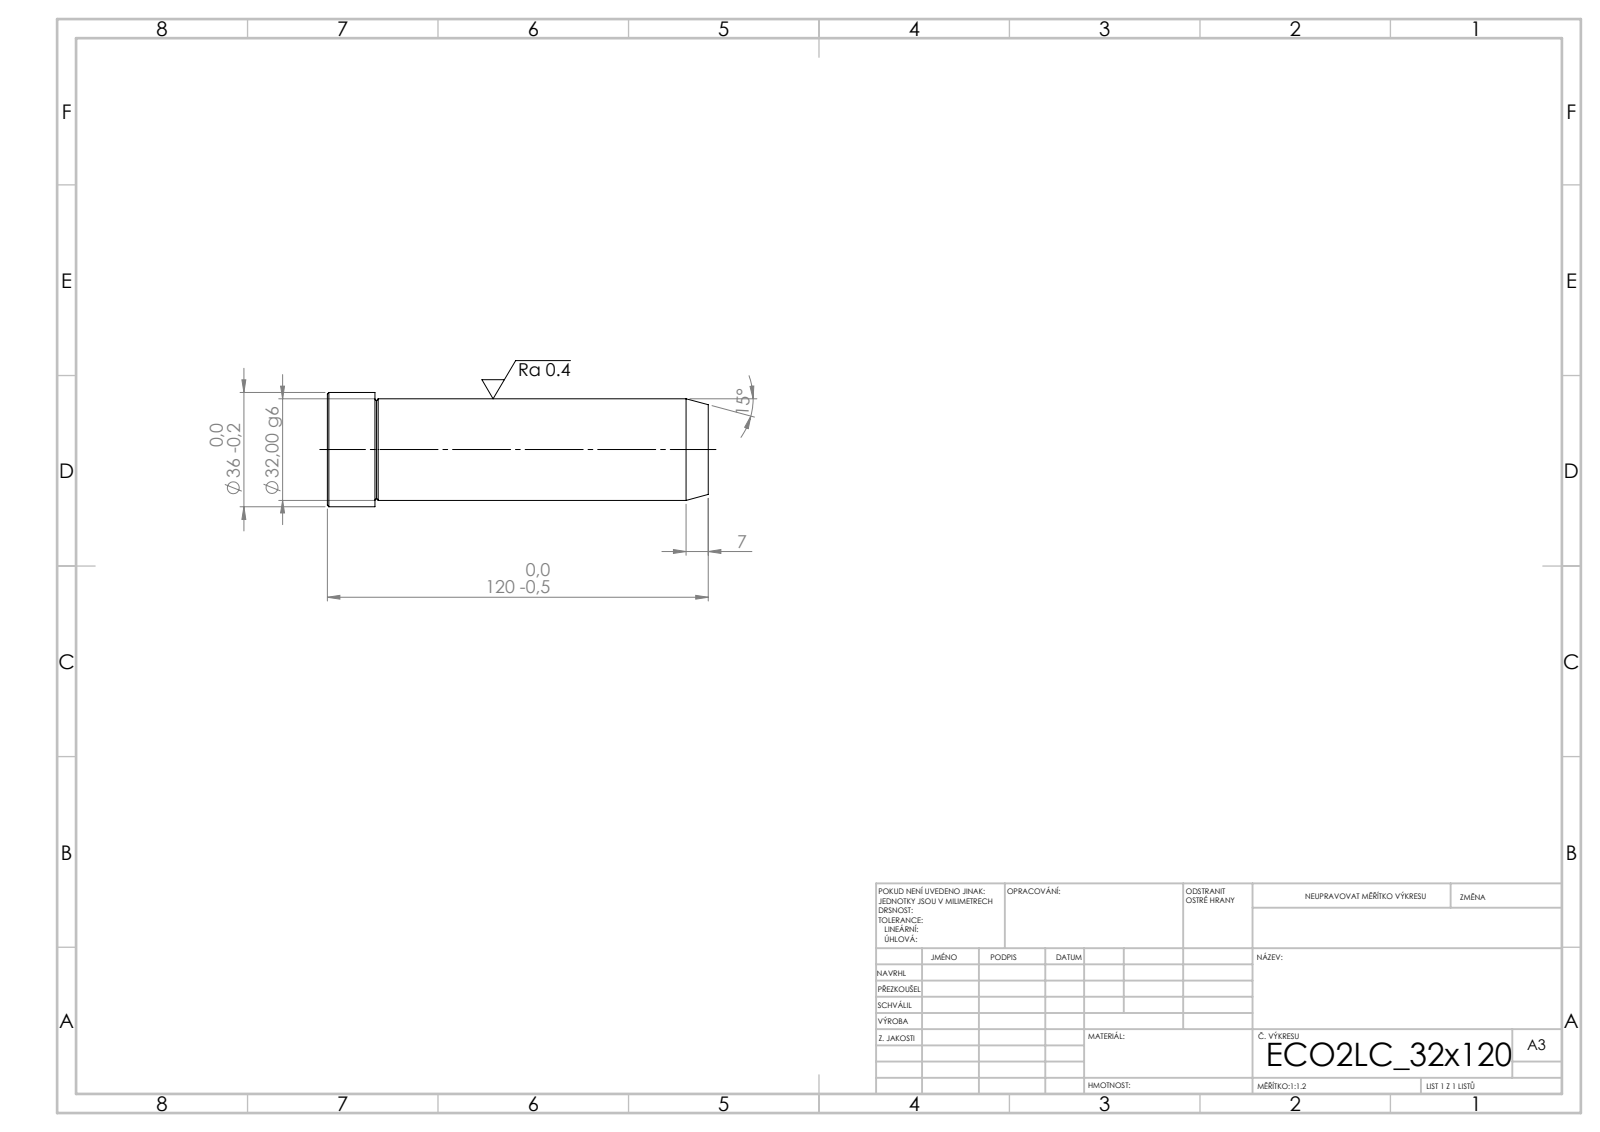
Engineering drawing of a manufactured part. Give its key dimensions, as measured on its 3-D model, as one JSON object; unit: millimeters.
{"step_written_by": "SolidWorks 2019 (CONFIG_CONTROL_DESIGN)", "units": "millimeters", "bodies": {"solids": 1, "faces": 15, "planar": 3, "cylindrical": 4, "other": 8}, "overall_size": [120, 36, 36], "volume_mm3": 99027, "surface_area_mm2": 14113, "round_bosses_or_shafts": [[36, 1], [32, 1]], "face_to_face_distances": [120, 105, 15]}
